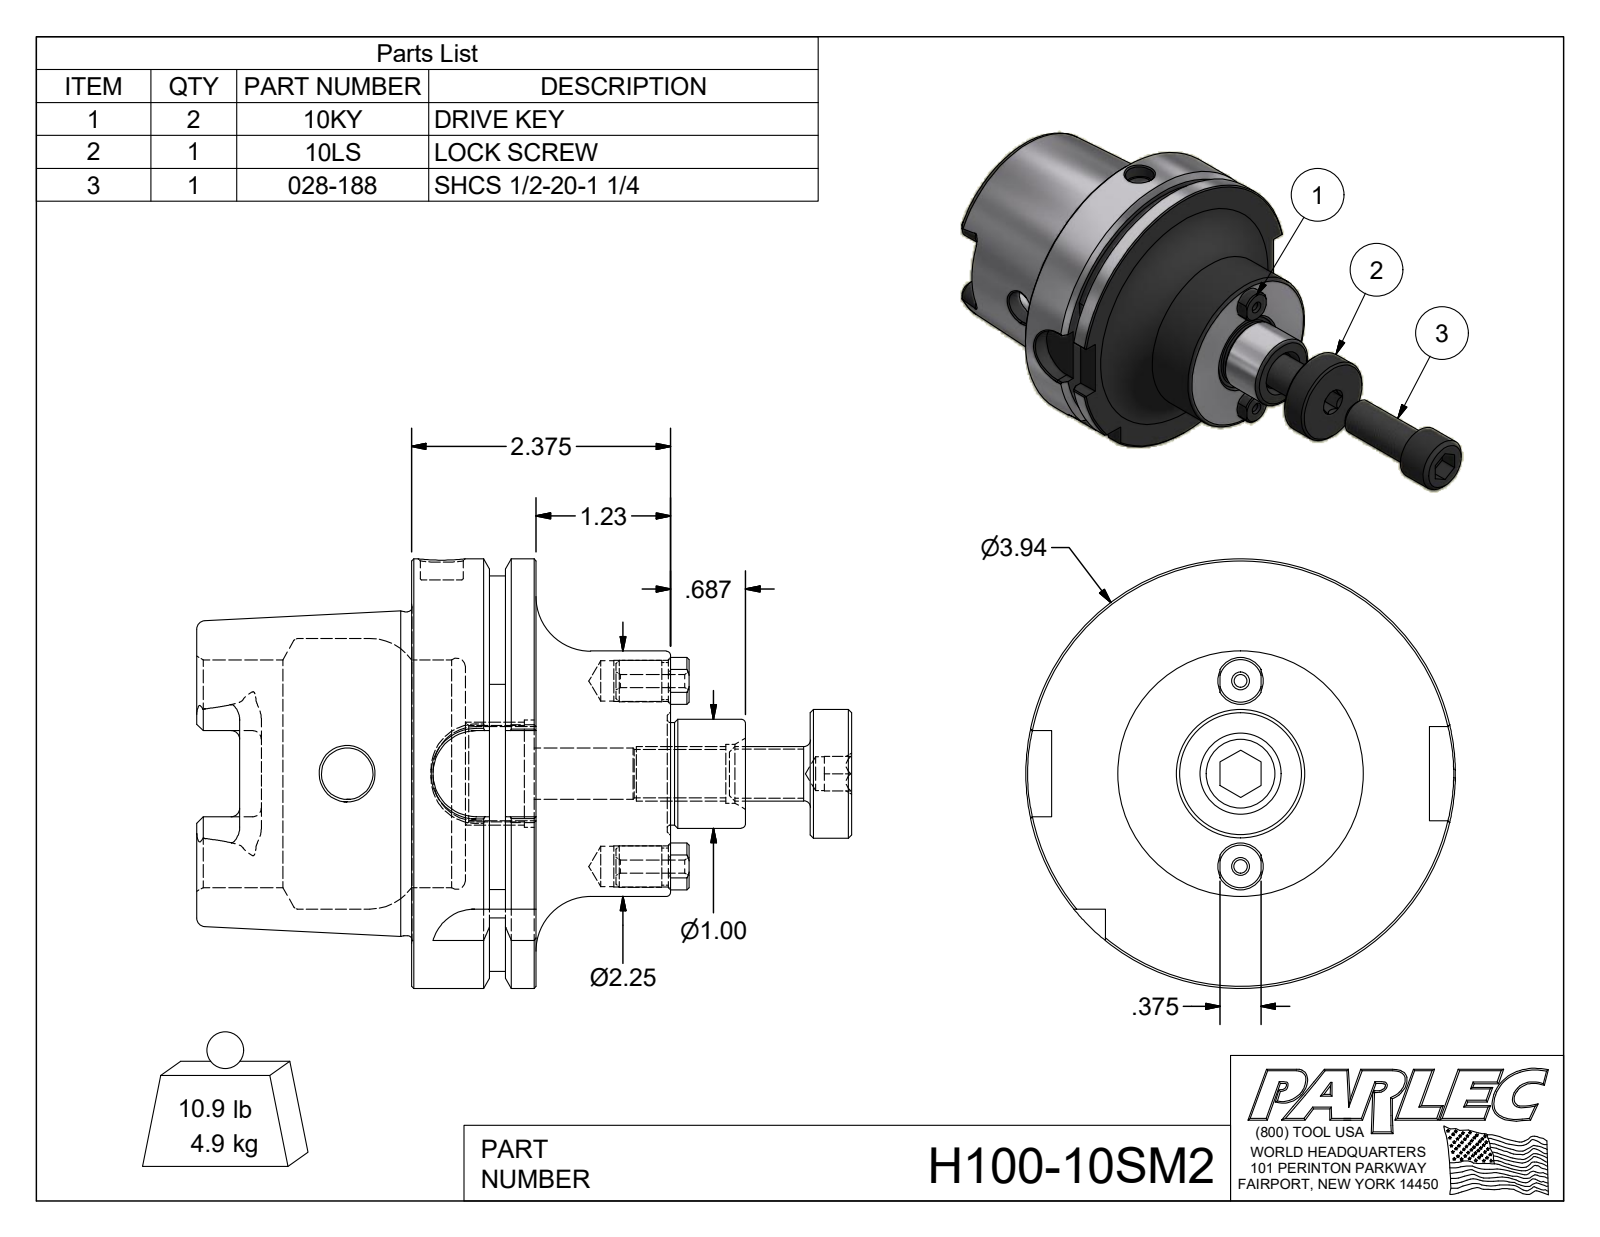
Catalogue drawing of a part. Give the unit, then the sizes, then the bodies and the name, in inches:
Units: inches
Overall size (bounding box): 8.179 × 3.937 × 3.937
Round holes (diameter × count): ⌀0.12 ×2, ⌀0.368 ×2, ⌀0.374 ×2, ⌀0.472 ×2, ⌀0.312 ×1, ⌀0.394 ×1, ⌀0.446 ×1, ⌀0.54 ×1, ⌀0.881 ×1, ⌀0.985 ×1, ⌀2.087 ×1, ⌀2.48 ×1
Round bosses / shafts (diameter × count): ⌀0.38 ×2, ⌀0.34 ×2, ⌀3.937 ×1, ⌀2.967 ×1, ⌀2.25 ×1, ⌀1.18 ×1, ⌀1 ×1, ⌀0.94 ×1
Partial cylindrical surfaces — rounded edges, fillets, slot ends (radius × count): R0.079 ×6, R0.192 ×4, R0.394 ×4, R0.214 ×2, R1.811 ×1
Main face-to-face distances: 1.142, 0.492, 2.375, 1.233, 0.65, 1.883, 1.969, 2.461, 3.11, 4.344
Hole centre spacings: 0.85, 1.7
Volume: 21.94 in³ · Surface area: 102.8 in²
Bodies: 5 solids, 212 faces (79 planar, 55 cylindrical, 78 other)
Part name (STEP PRODUCT): H100-10SM2; 10KY; 10LS; 028-188
STEP written by: Autodesk Inventor 2012 (AUTOMOTIVE_DESIGN)
